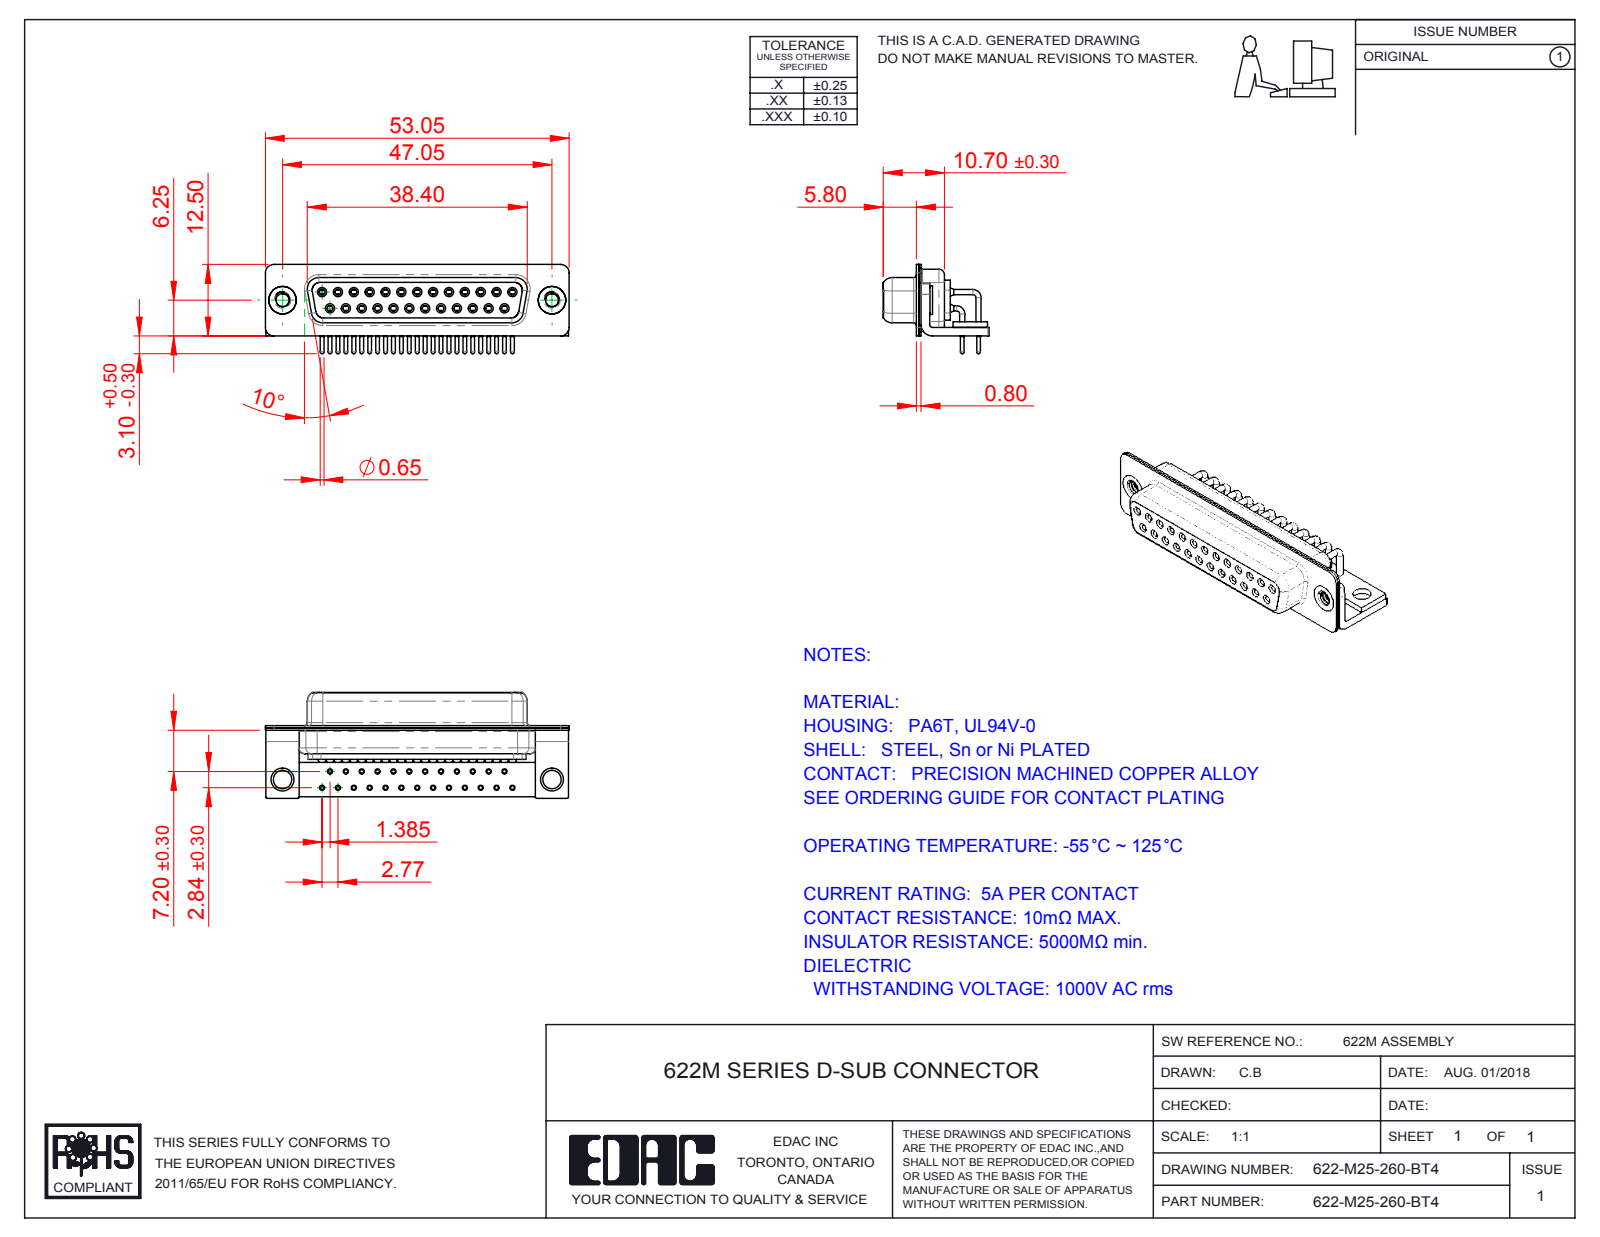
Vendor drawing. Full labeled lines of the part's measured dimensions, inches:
Part name (STEP PRODUCT): 622M Stabilizer Board_25 Contacts; 622M 4-40 Threaded Rivet_Stabilizer; 622M Stabilizer Bracket; 622-M25-260-BT4 (+5 more)
STEP written by: SolidWorks 2016 (CONFIG_CONTROL_DESIGN)
Units: inches
Bodies: 33 solids, 1704 faces (468 planar, 784 cylindrical, 452 other)
Overall size (bounding box): 2.089 × 0.728 × 0.614
Volume: 0.266 in³ · Surface area: 16.74 in²
Round holes (diameter × count): ⌀0.035 ×25, ⌀0.039 ×25, ⌀0.043 ×25, ⌀0.067 ×25, ⌀0.071 ×25, ⌀0.079 ×25, ⌀0.089 ×2, ⌀0.126 ×2, ⌀0.157 ×2, ⌀0.189 ×2
Round bosses / shafts (diameter × count): ⌀0.035 ×27, ⌀0.063 ×25, ⌀0.059 ×25, ⌀0.026 ×25, ⌀0.197 ×2, ⌀0.193 ×2
Partial cylindrical surfaces — rounded edges, fillets, slot ends (radius × count): R0.01 ×16, R0.059 ×16, R0.079 ×13, R0.053 ×8, R0.063 ×8, R0.02 ×5, R0.024 ×4, R0.026 ×4
Main face-to-face distances: 0.016, 0.091, 0.075, 0.057, 0.352, 0.033, 0.031, 0.244, 0.039, 0.368
Hole centre spacings: 0.124, 0.109, 0.218, 0.327, 0.436, 0.545, 0.654, 0.198
